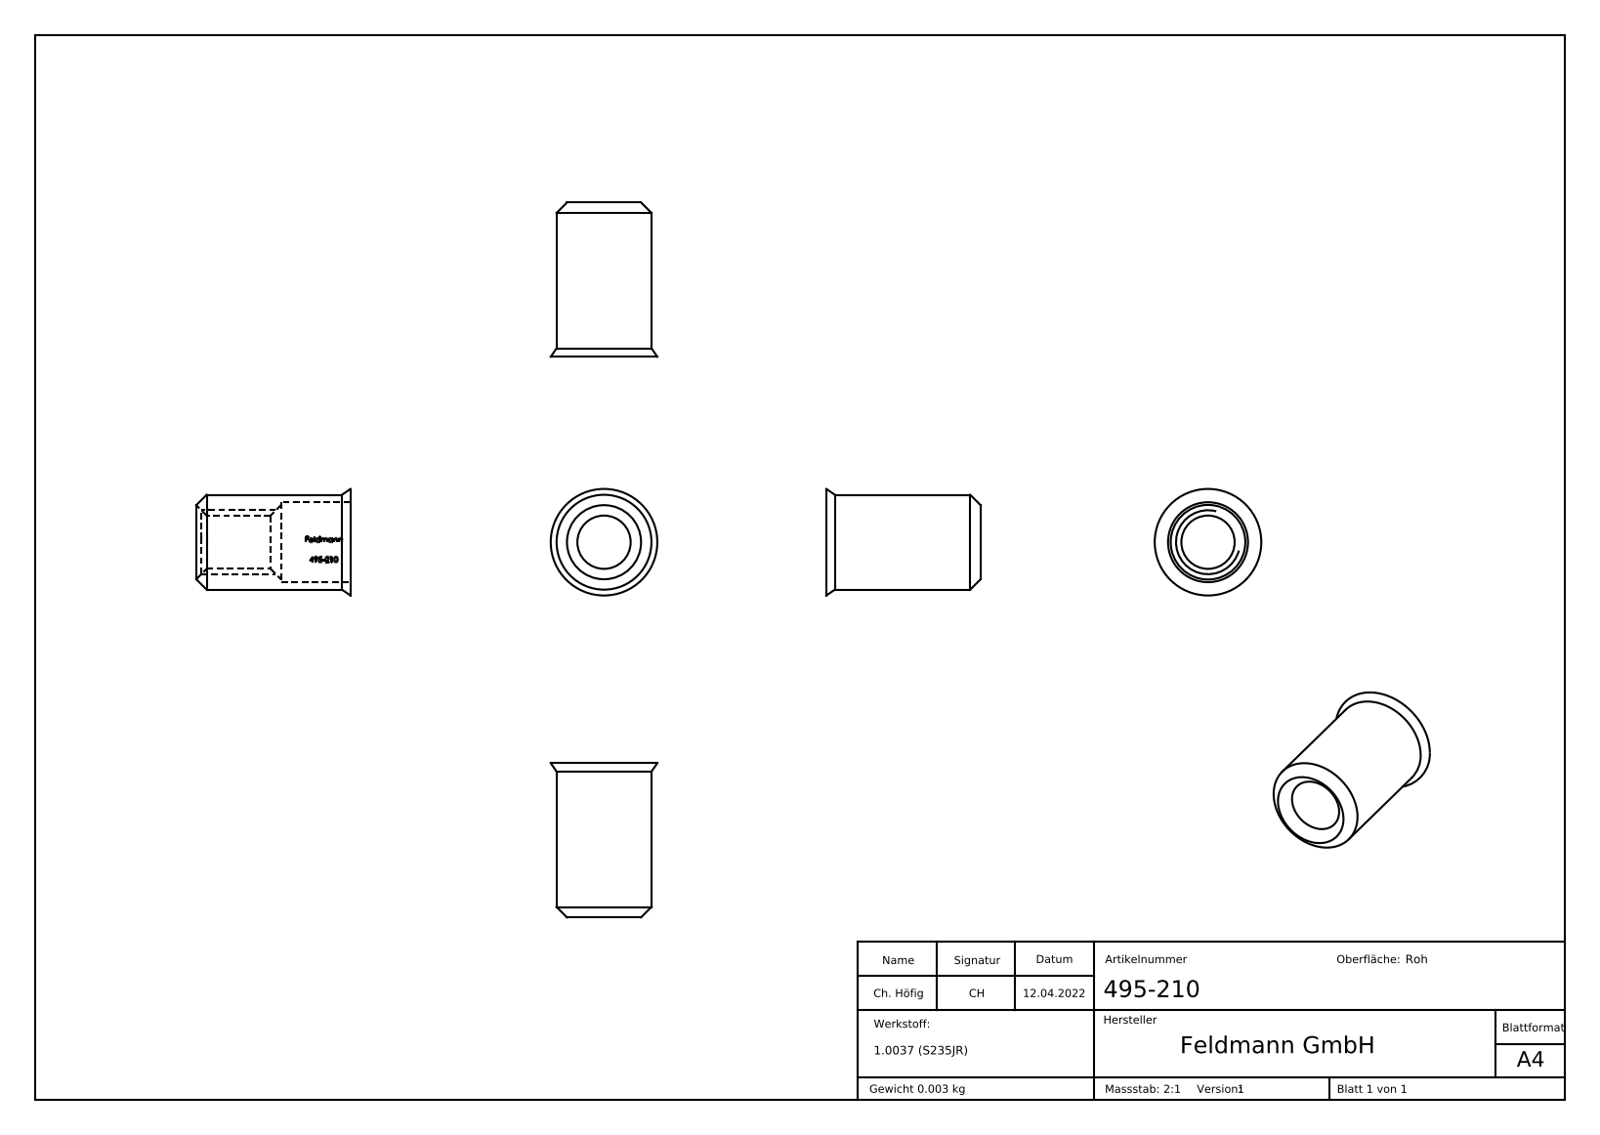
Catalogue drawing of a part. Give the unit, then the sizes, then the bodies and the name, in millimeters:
Units: millimetres
Overall size (bounding box): 14.47 × 10 × 10
Round holes (diameter × count): ⌀5 ×1, ⌀7.5 ×1
Round bosses / shafts (diameter × count): ⌀8.9 ×1
Partial cylindrical surfaces — rounded edges, fillets, slot ends (radius × count): R3.85 ×1
Main face-to-face distances: 6.5, 1.83, 0.66, 1.35, 1.88, 1.19, 1.74, 1.67, 1.62, 2.29
Volume: 433 mm³ · Surface area: 762 mm²
Bodies: 1 solid, 210 faces (100 planar, 29 cylindrical, 81 other)
Part name (STEP PRODUCT): 495-210
STEP written by: SolidWorks 2018 (CONFIG_CONTROL_DESIGN)
